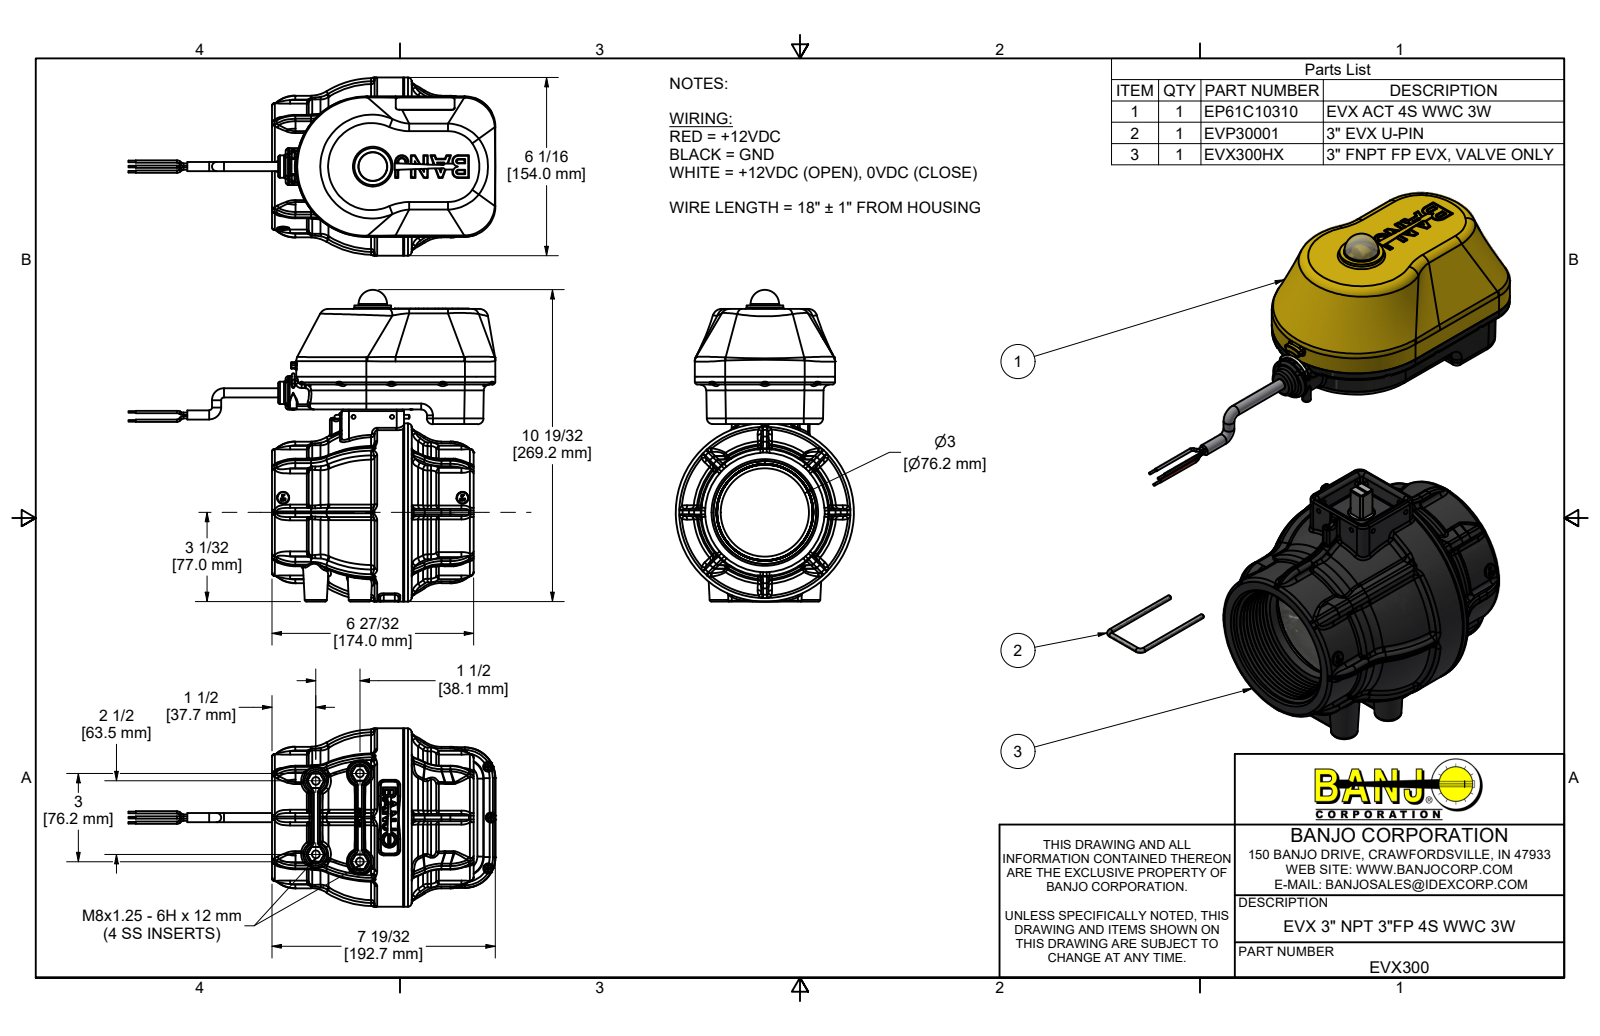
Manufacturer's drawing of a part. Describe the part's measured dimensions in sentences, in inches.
The part is named "EVX300; EP61C10310; B61905PPHS; B632038PM (+8 more)". Its 3-D file was written by "Autodesk Inventor 2022 (AUTOMOTIVE_DESIGN)". It is 78 solids with 9137 faces: 3033 planar, 3295 cylindrical and 2809 other. Overall it measures 12.476 by 10.6 by 6.063 inches. Its volume is 96.36 cubic inches and its surface area 930 square inches. Round holes: 15 of diameter 0.15, 11 of diameter 0.095, 11 of diameter 0.34, 7 of diameter 0.08, 5 of diameter 0.135, 4 of diameter 0.104, 4 of diameter 0.136, 4 of diameter 0.148, 4 of diameter 0.176, 4 of diameter 0.262, 4 of diameter 0.266, 4 of diameter 0.433. Round bosses or shafts: 19 of diameter 0.25, 15 of diameter 0.08, 11 of diameter 0.14, 11 of diameter 0.108, 11 of diameter 0.085, 6 of diameter 0.058, 5 of diameter 0.375, 4 of diameter 0.437. Partial cylindrical surfaces (rounded edges, fillets, slot ends): 204 of radius 0.013, 138 of radius 0.405, 114 of radius 0.387, 112 of radius 0.309, 111 of radius 0.01, 108 of radius 0.253, 106 of radius 0.609, 76 of radius 0.125. The main face-to-face distances are 0.083, 0.5, 0.085, 0.125, 0.181, 0.096, 2.175, 2.356, 2.271, 2.481. The hole center spacings are 2.272, 3.316, 1.313, 2.426, 3.247, 4.245, 0.55, 0.646.
